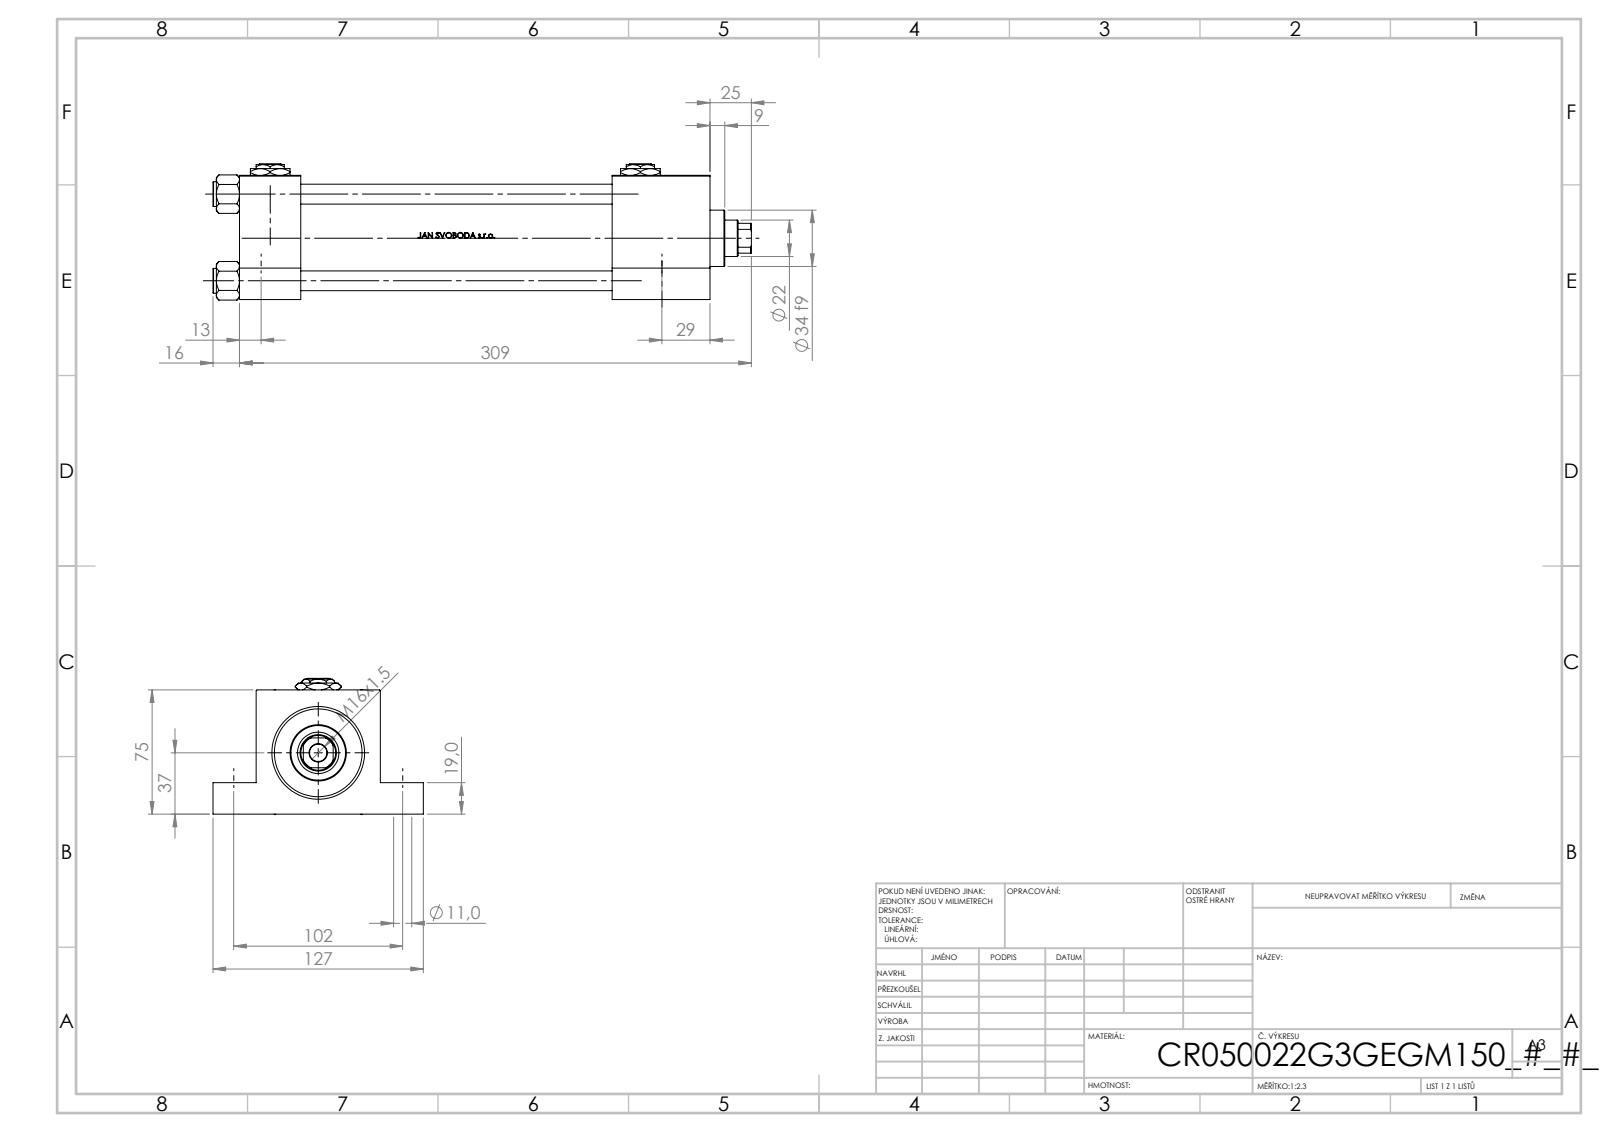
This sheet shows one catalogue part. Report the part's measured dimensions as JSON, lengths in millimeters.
{"part_name": "V215CR_VCP_G; V215_VC_A; V215CR_G_TYCINKA; Zatka_pro_OIL_PORT (+2 more)", "step_written_by": "SolidWorks 2019 (CONFIG_CONTROL_DESIGN)", "units": "millimeters", "bodies": {"solids": 17, "faces": 1252, "planar": 496, "cylindrical": 136, "other": 620}, "overall_size": [325, 127, 82.27], "volume_mm3": 994355, "surface_area_mm2": 258057, "round_holes": [[12, 4], [14, 4], [7, 2], [20.96, 2], [30, 2], [10.5, 1], [22, 1], [25, 1], [41, 1], [50, 1], [53, 1]], "round_bosses_or_shafts": [[15, 4], [56, 1], [34, 1]], "partial_cylinders_radius": [[10.5, 1]], "face_to_face_distances": [75, 37, 284, 247, 19, 225, 56, 188, 59, 26], "hole_center_spacings": [36.98, 52.3, 51.3, 52.63, 73.96, 102, 234.61, 241.94]}
